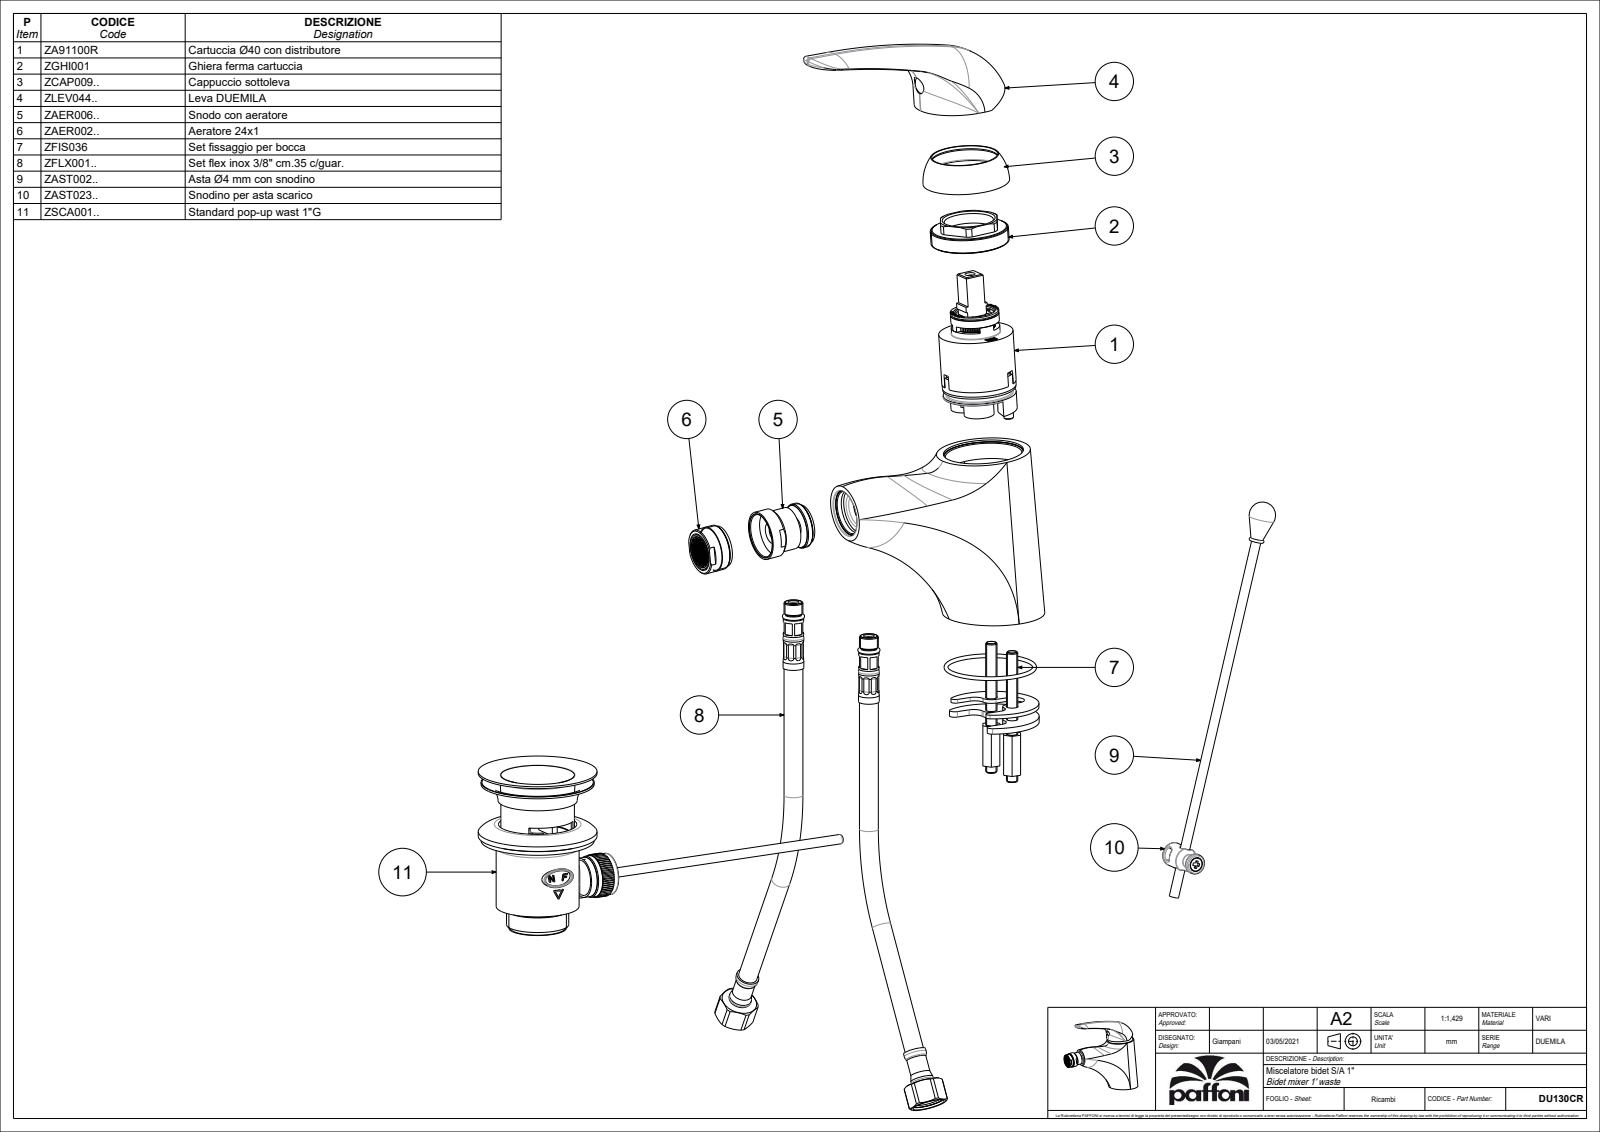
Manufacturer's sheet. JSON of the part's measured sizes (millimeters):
{"part_name": "DU135CR", "step_written_by": "CREO PARAMETRIC BY PTC INC, 2020044 (CONFIG_CONTROL_DESIGN)", "units": "millimeters", "bodies": {"solids": 5, "faces": 2771, "planar": 2039, "cylindrical": 413, "other": 319}, "overall_size": [164.45, 132.2, 54.3], "volume_mm3": 194736, "surface_area_mm2": 108133, "round_holes": [[8, 5], [11, 3], [3.3, 2], [4.6, 2], [5.5, 2], [7, 2], [9, 2], [12, 2], [16, 2], [21, 2], [4, 1], [5, 1]], "round_bosses_or_shafts": [[10, 3], [8, 3], [25.8, 2], [24, 2], [15.9, 2], [9.4, 2], [8.2, 2], [6, 2]], "partial_cylinders_radius": [[0.5, 57], [0.2, 28], [1.5, 12], [7.5, 6], [0.3, 4], [5, 3], [1, 2], [5.5, 2]], "face_to_face_distances": [3.5, 13.01, 10, 4.5, 1, 6.5, 5.5, 9.51, 20, 0.5], "hole_center_spacings": [8.61, 14, 2, 9.91, 13.04, 14.14, 1.3, 5.99]}
